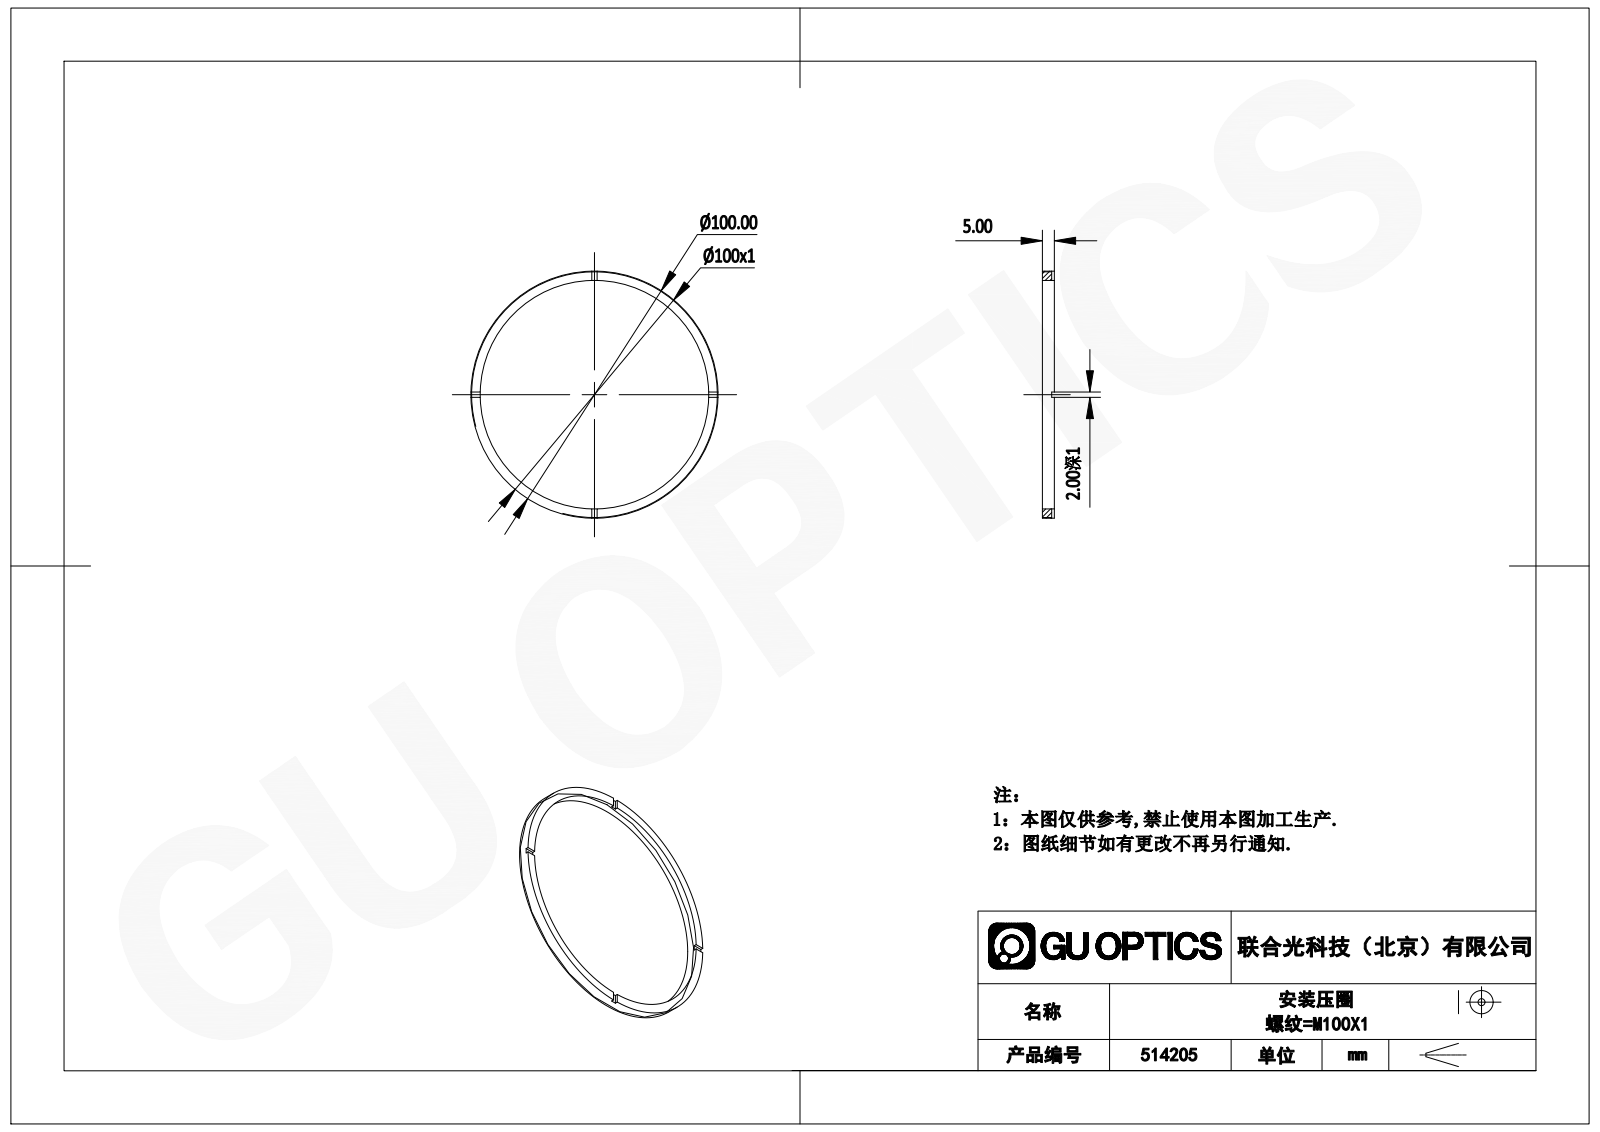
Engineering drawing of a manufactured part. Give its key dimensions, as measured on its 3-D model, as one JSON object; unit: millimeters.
{"part_name": "514205", "step_written_by": "SolidWorks 2020 (CONFIG_CONTROL_DESIGN)", "units": "millimeters", "bodies": {"solids": 1, "faces": 21, "planar": 17, "cylindrical": 4, "other": 0}, "overall_size": [100, 100, 5], "volume_mm3": 6000, "surface_area_mm2": 5445, "round_holes": [[92, 1]], "round_bosses_or_shafts": [[100, 1]], "face_to_face_distances": [5, 4, 1, 2]}
